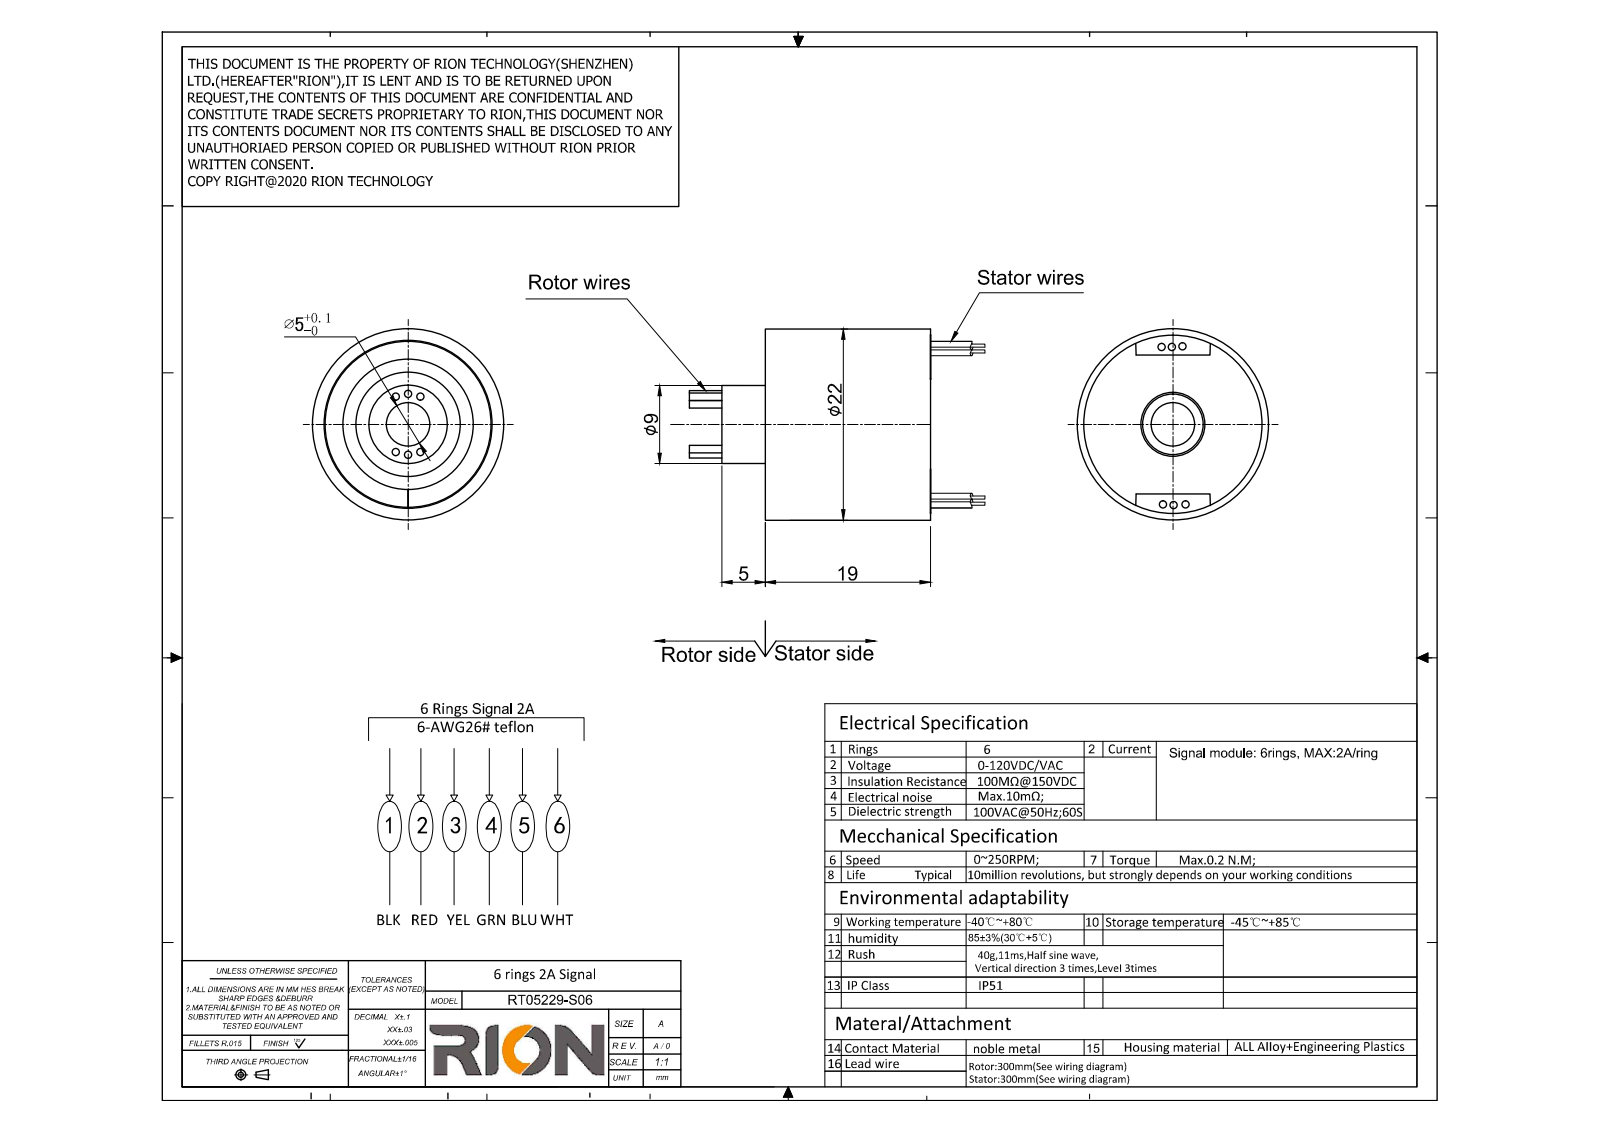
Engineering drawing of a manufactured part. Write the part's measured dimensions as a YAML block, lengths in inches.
part_name: "RT05229-S06"
step_written_by: "SolidWorks 2014 (CONFIG_CONTROL_DESIGN)"
units: inches
bodies: {solids: 1, faces: 77, planar: 31, cylindrical: 46, other: 0}
overall_size: [1.319, 0.866, 0.866]
volume: 0.432
surface_area: 4.945
round_holes:
  - {diameter: 0.197, count: 1}
  - {diameter: 0.283, count: 1}
  - {diameter: 0.48, count: 1}
  - {diameter: 0.76, count: 1}
round_bosses_or_shafts:
  - {diameter: 0.031, count: 12}
  - {diameter: 0.866, count: 1}
  - {diameter: 0.756, count: 1}
  - {diameter: 0.472, count: 1}
  - {diameter: 0.354, count: 1}
  - {diameter: 0.276, count: 1}
face_to_face_distances: [0.748, 0.197, 0.945, 0.02, 0.925, 0.728, 0.039, 0.669, 0.709, 1.122]
